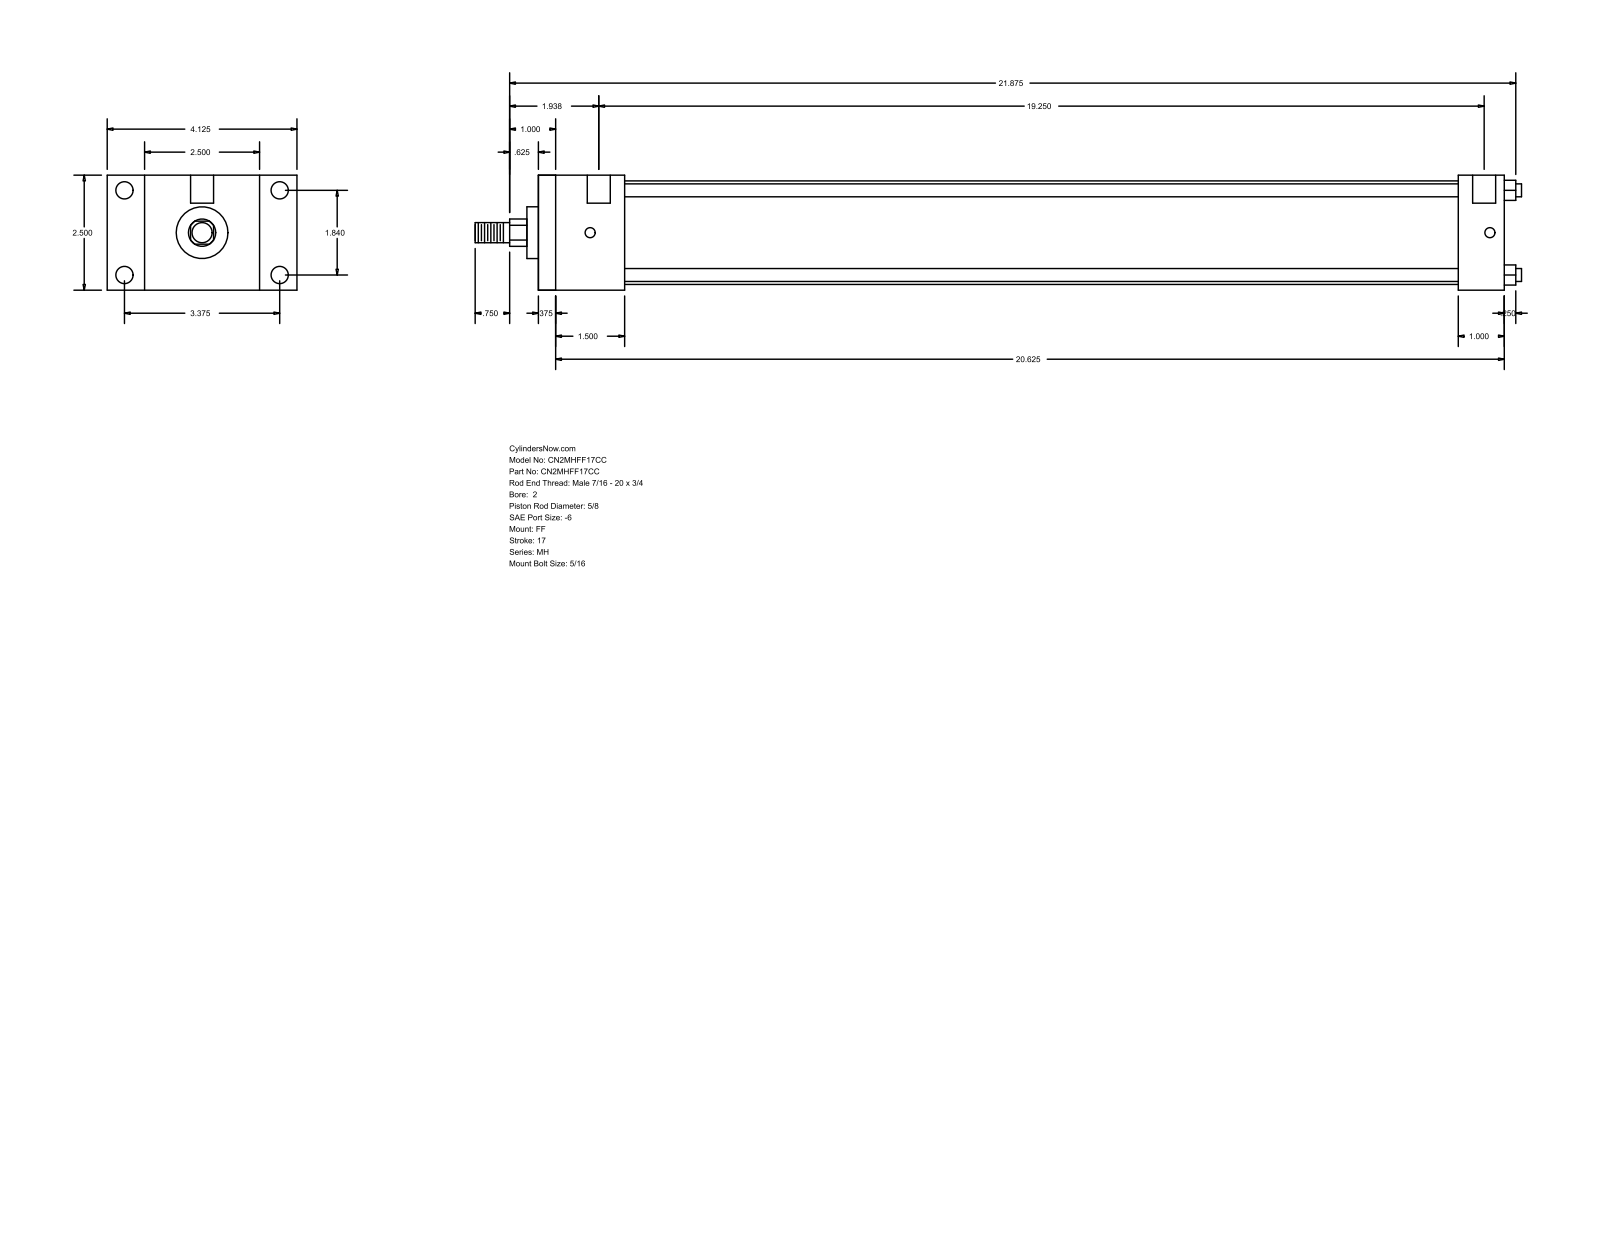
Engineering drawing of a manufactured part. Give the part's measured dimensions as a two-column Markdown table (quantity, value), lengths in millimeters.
| quantity | value |
| --- | --- |
| part name | MH_FF__0200_0.625 |
| STEP written by | GSSL Pune (CONFIG_CONTROL_DESIGN) |
| units | millimeters |
| bodies | 0 solids, 92 faces (64 planar, 28 cylindrical, 0 other) |
| overall size | 577.85 × 104.78 × 63.5 |
| round holes (diameter × count) | 5.56 × 4, 9.53 × 4, 12.7 × 2 |
| round bosses / shafts (diameter × count) | 7.14 × 4, 57.15 × 1, 28.57 × 1, 15.88 × 1, 11.11 × 1 |
| partial cylindrical surfaces (radius × count) | 7.54 × 1 |
| main face-to-face distances | 63.5, 533.39, 9.52, 523.87, 38.1, 47.62, 508, 498.48, 460.38, 485.77 |
| hole center spacings | 46.74, 85.72, 97.63, 496.89, 3.18, 4.76, 488.95, 492.13 |
